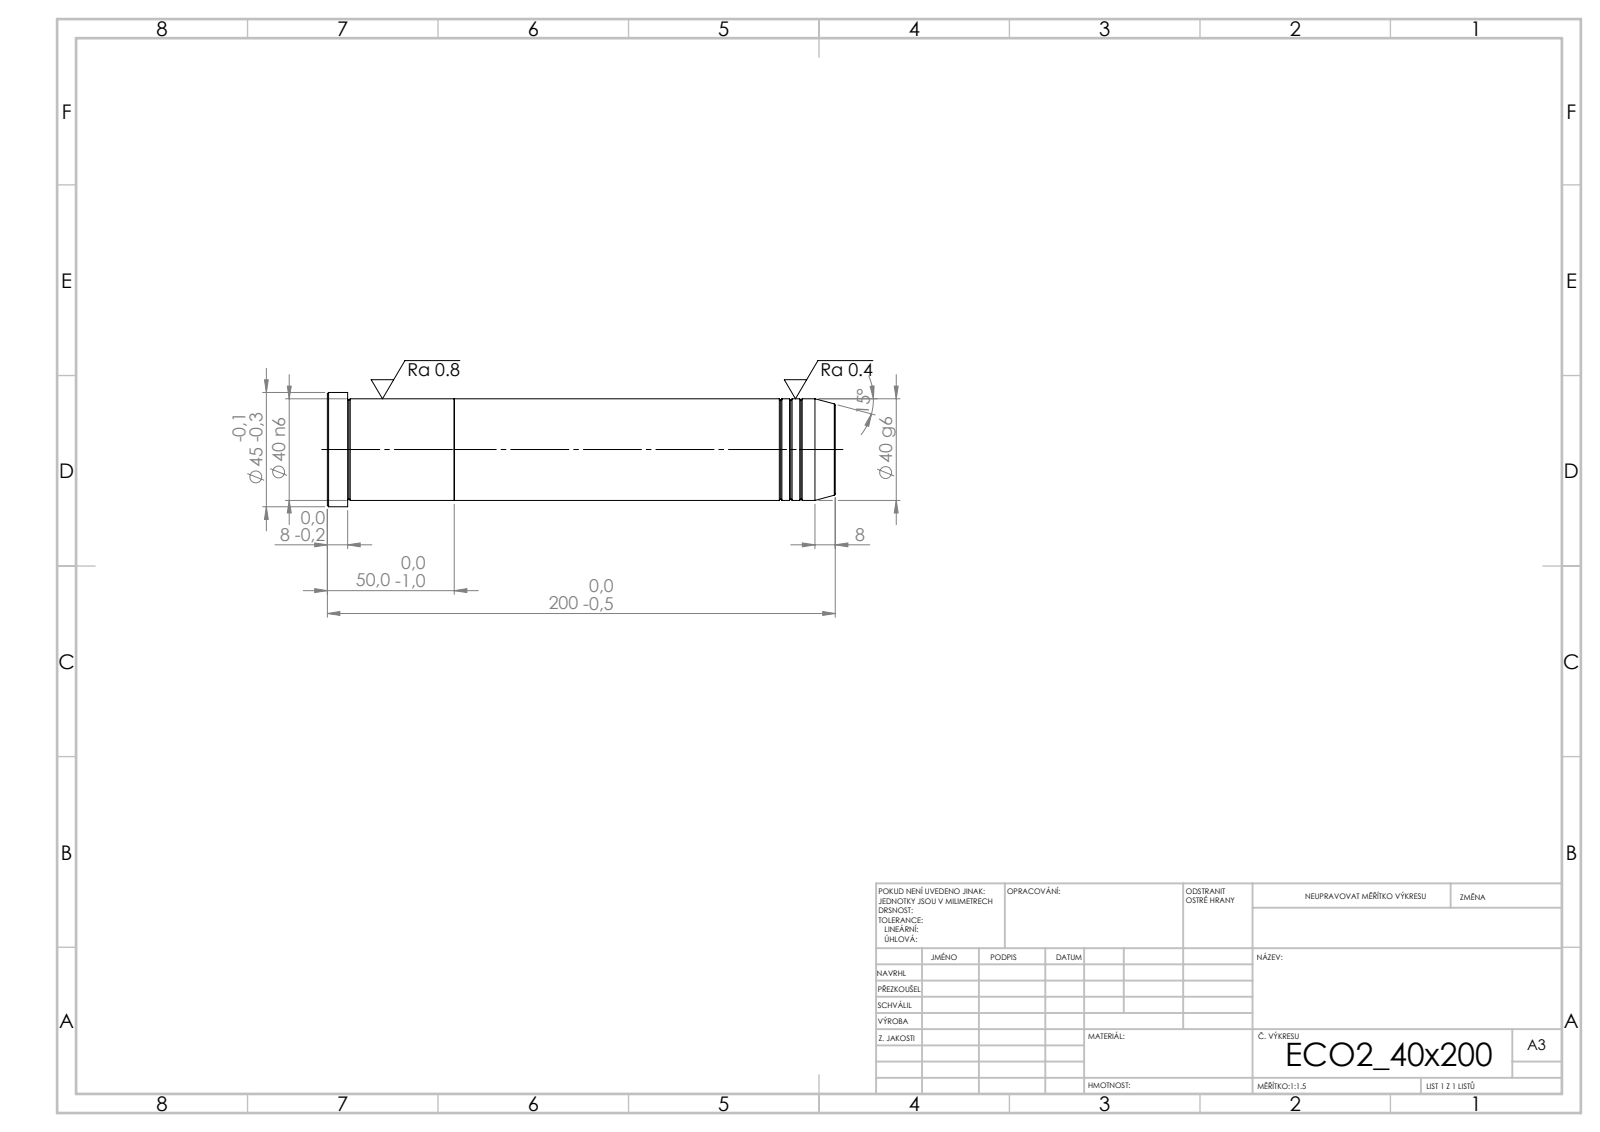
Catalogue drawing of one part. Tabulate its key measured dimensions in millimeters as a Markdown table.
| quantity | value |
| --- | --- |
| STEP written by | SolidWorks 2019 (CONFIG_CONTROL_DESIGN) |
| units | millimeters |
| bodies | 2 solids, 39 faces (5 planar, 12 cylindrical, 22 other) |
| overall size | 200 × 45 × 45 |
| volume | 252 743 mm³ |
| surface area | 30 897 mm² |
| round bosses / shafts (diameter × count) | 45 × 1, 40 × 1 |
| main face-to-face distances | 50, 150, 200, 192, 42, 8 |
